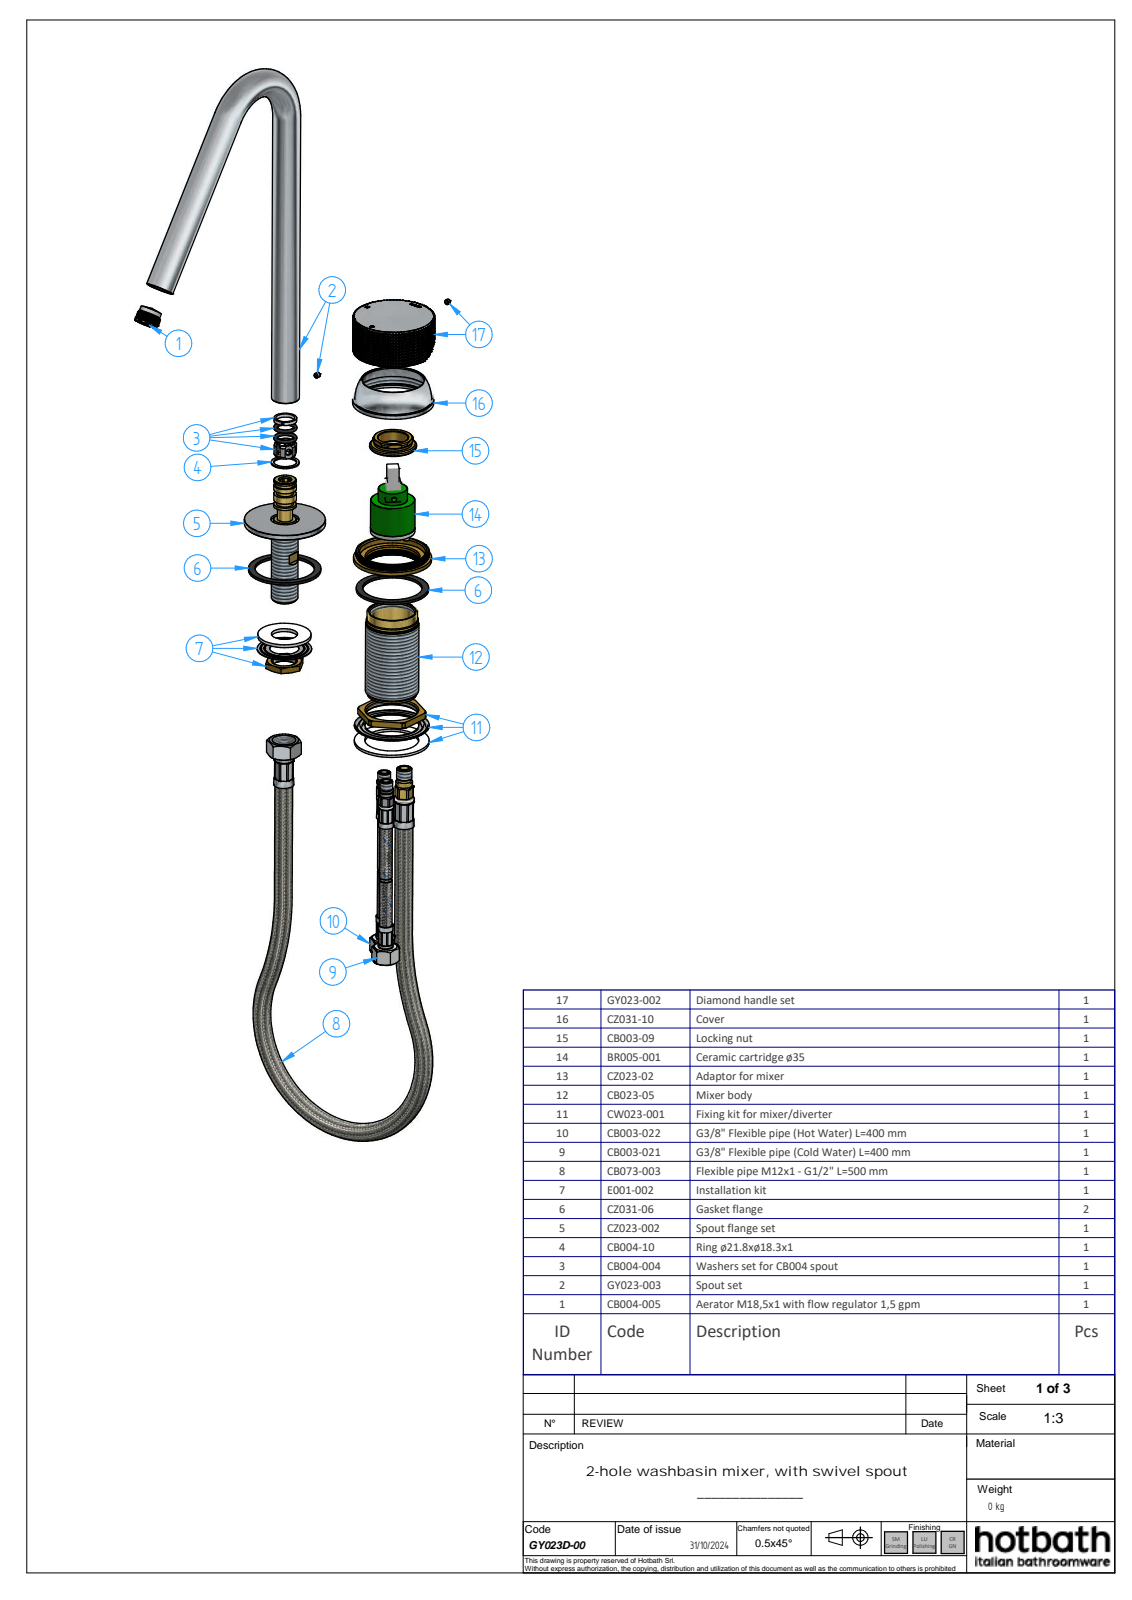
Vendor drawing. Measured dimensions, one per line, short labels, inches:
name: GY023D-00; CZ023-002_oa_0; CZ023-01; GY023-003 (+6 more)
written by: Solid Edge (AUTOMOTIVE_DESIGN)
unit: in
bodies: 6 solids, 6923 faces (2303 planar, 3574 cylindrical, 1046 other)
size: 203.162 × 199.127 × 199.127
volume: 4 167 000 in³; area: 125 400 in²
holes: 116× ⌀0.03, 2× ⌀0.709, 2× ⌀2.303, 1× ⌀0.13, 1× ⌀0.165, 1× ⌀0.177, 1× ⌀0.433, 1× ⌀0.543, 1× ⌀0.551, 1× ⌀0.591, 1× ⌀0.63, 1× ⌀0.669
bosses: 2× ⌀2.52, 2× ⌀0.866, 1× ⌀0.984, 1× ⌀0.827, 1× ⌀0.724, 1× ⌀0.686, 1× ⌀0.685, 1× ⌀0.63
rounds: 318× R0.004, 1× R0.019, 1× R0.256
face distances: 1.134, 0.091, 1.224, 0.157, 0.067, 1.291, 2.339, 0.047, 0.11, 0.043
hole spacings: 0.121, 0.04, 0.047, 0.081, 0.082, 0.092, 0.121, 0.125
